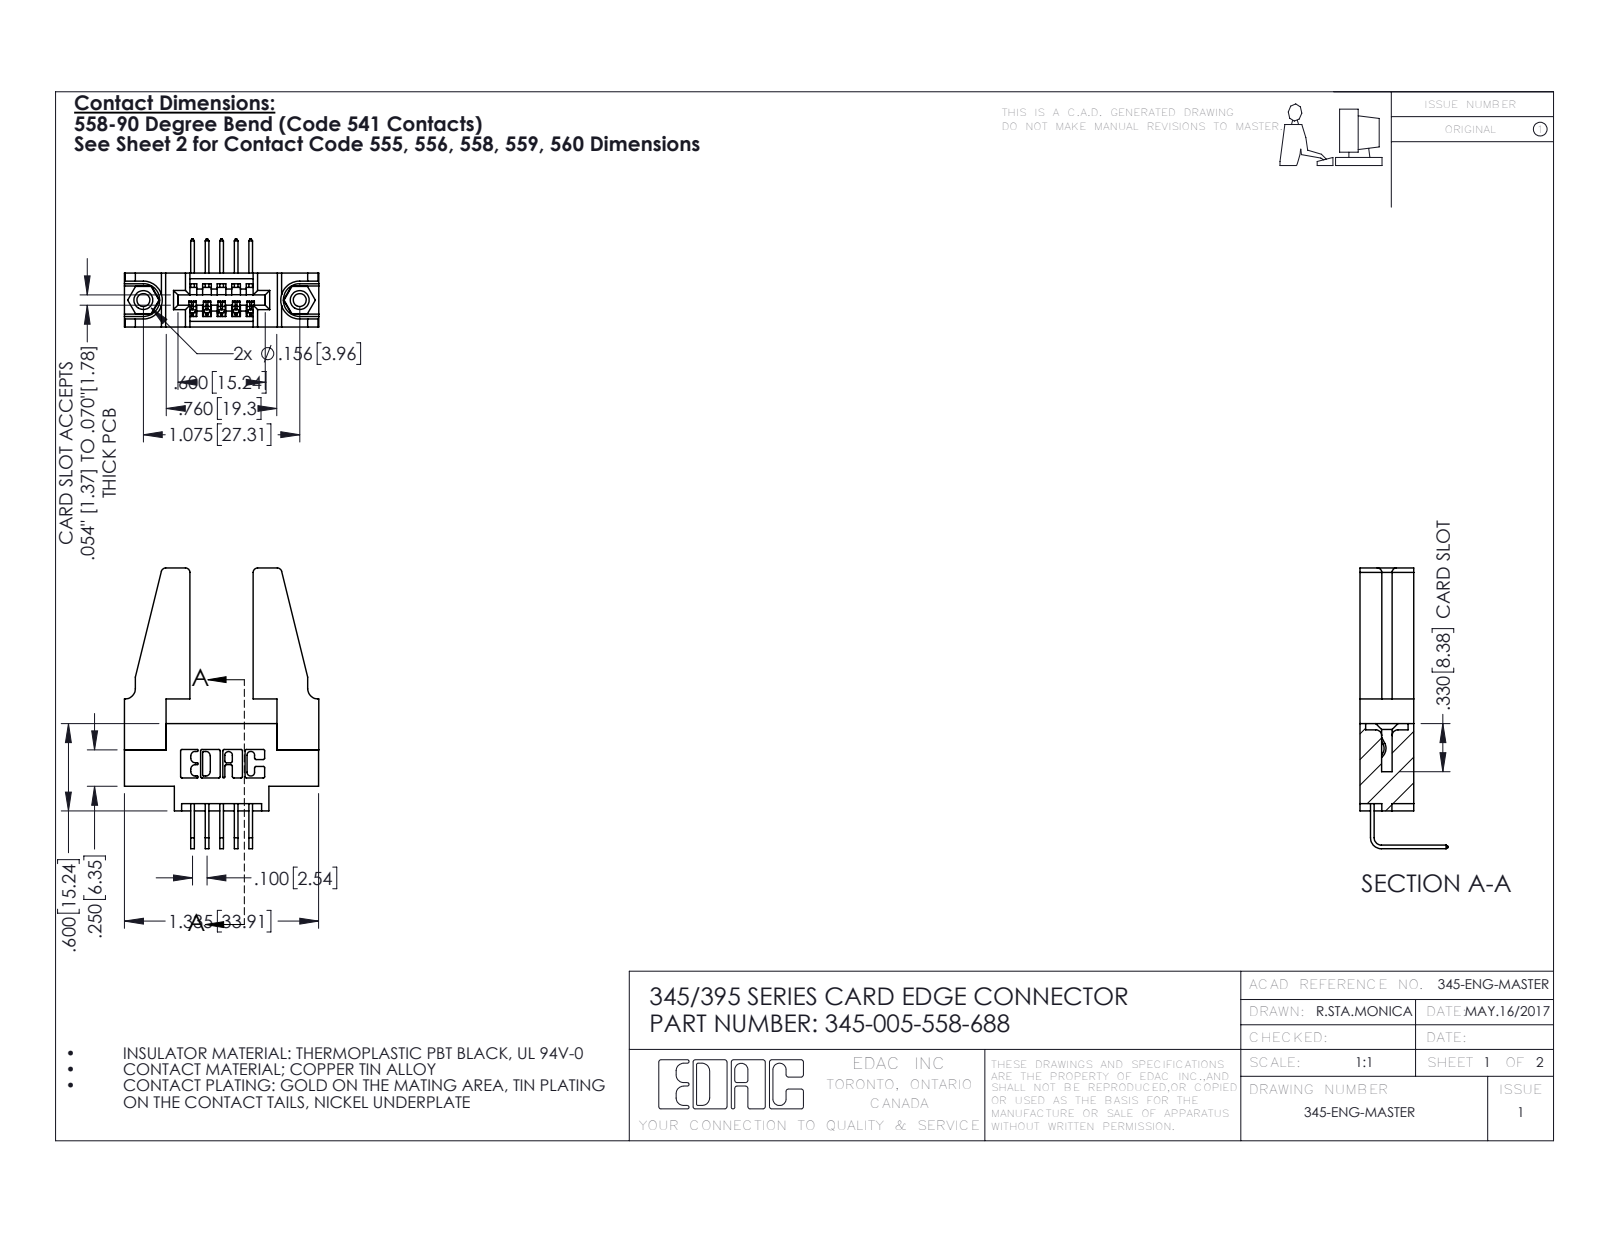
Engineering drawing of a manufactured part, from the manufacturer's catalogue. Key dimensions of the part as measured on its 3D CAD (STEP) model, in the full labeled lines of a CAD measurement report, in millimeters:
Part name (STEP PRODUCT): 345-005-558-688; 345-250-001_345-250-001-102; 345 Part_0.170 Offset - 0.156 Dia-TH; 345-292-001_558 Tail - 2 (+1 more)
STEP written by: SolidWorks 2016 (CONFIG_CONTROL_DESIGN)
Units: millimetres
Bodies: 10 solids, 554 faces (366 planar, 172 cylindrical, 16 other)
Overall size (bounding box): 49 × 33.9 × 15.4
Volume: 6 080 mm³ · Surface area: 6 600 mm²
Round holes (diameter × count): ⌀2.3 ×2, ⌀3.2 ×2, ⌀4 ×2, ⌀1.6 ×1
Round bosses / shafts (diameter × count): ⌀3.9 ×2
Partial cylindrical surfaces — rounded edges, fillets, slot ends (radius × count): R0.3 ×22, R0.2 ×10, R0.8 ×8, R0.2 ×6, R0.8 ×6, R0.7 ×3, R0.8 ×2, R1 ×2
Main face-to-face distances: 9.4, 1.8, 7.6, 5.1, 3.8, 3.8, 5.6, 2, 11, 2.5
Hole centre spacings: 6.9, 21.5, 27.3
